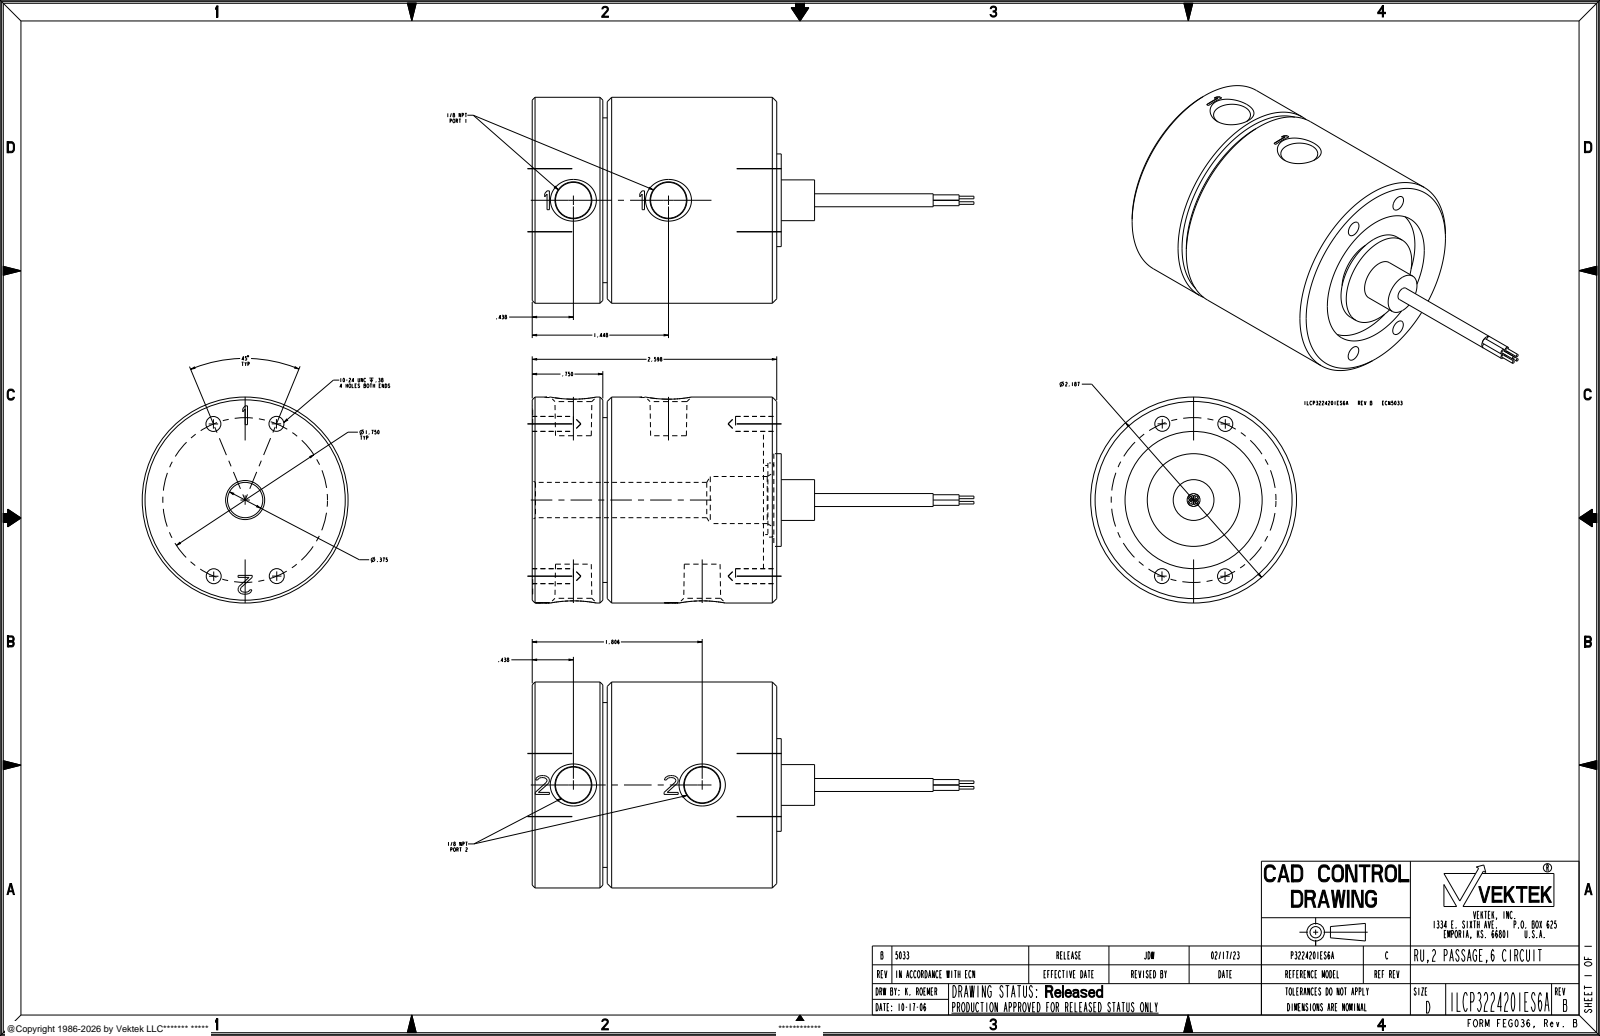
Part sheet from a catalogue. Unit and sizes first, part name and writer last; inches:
Units: inches
Overall size (bounding box): 4.693 × 2.187 × 2.187
Round holes (diameter × count): ⌀0.159 ×4, ⌀0.375 ×1, ⌀0.5 ×1, ⌀1.457 ×1
Round bosses / shafts (diameter × count): ⌀0.056 ×4, ⌀0.028 ×4, ⌀2.187 ×1, ⌀1.75 ×1, ⌀0.984 ×1, ⌀0.787 ×1, ⌀0.733 ×1, ⌀0.433 ×1
Main face-to-face distances: 2.598, 2.457, 0.141, 1.707, 0.75, 1.848, 0.047, 0.797, 1.66, 1.801
Hole centre spacings: 0.67, 0.875, 0.875, 1.617, 1.75, 1.75
Volume: 9.009 in³ · Surface area: 37.74 in²
Bodies: 1 solid, 246 faces (128 planar, 70 cylindrical, 48 other)
Part name (STEP PRODUCT): ILCP3224201ES6A
STEP written by: CREO PARAMETRIC BY PTC INC, 2021164 (AUTOMOTIVE_DESIGN)
